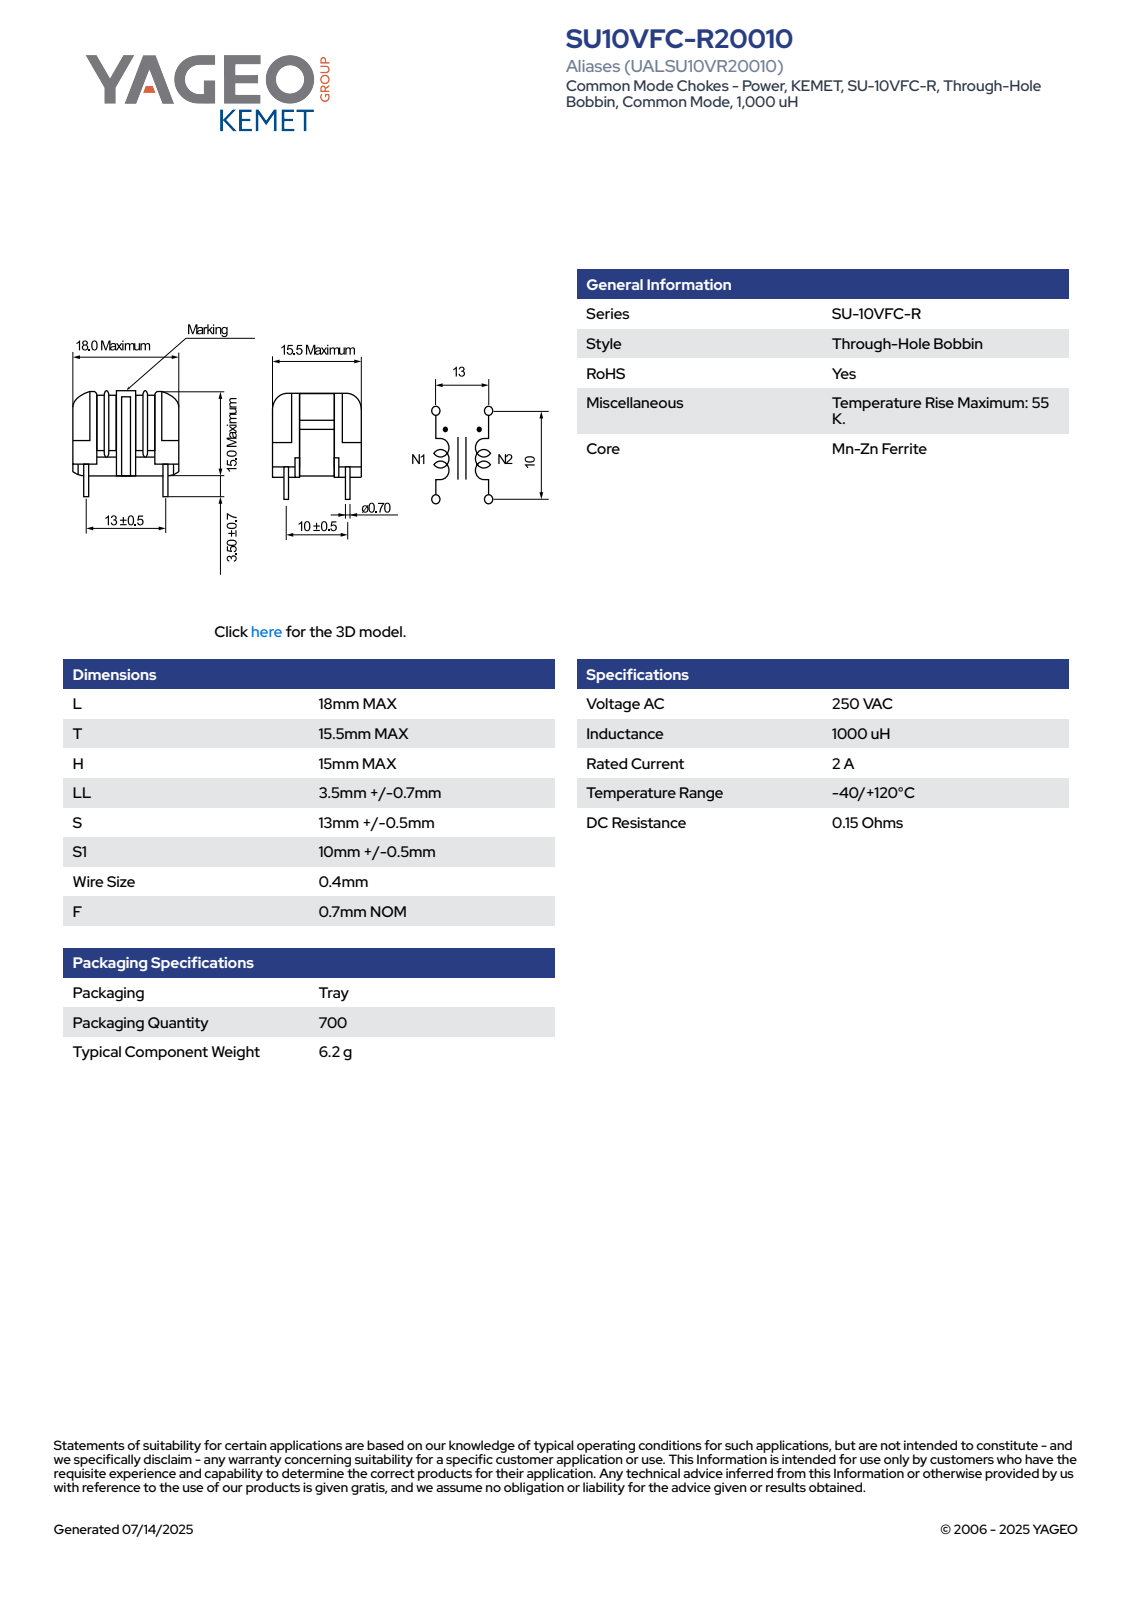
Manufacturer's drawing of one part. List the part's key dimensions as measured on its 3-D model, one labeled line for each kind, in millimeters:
Part name (STEP PRODUCT): SU10VFC(MAX-LOGO)
STEP written by: SolidWorks 2018 (AUTOMOTIVE_DESIGN)
Units: millimetres
Bodies: 2 solids, 912 faces (302 planar, 394 cylindrical, 216 other)
Overall size (bounding box): 18.5 × 18 × 15.5
Volume: 2 381 mm³ · Surface area: 3 995 mm²
Round bosses / shafts (diameter × count): ⌀0.7 ×4
Partial cylindrical surfaces — rounded edges, fillets, slot ends (radius × count): R0.5 ×60, R0.2 ×48, R0.23 ×48, R0.3 ×38, R0.8 ×10, R0.55 ×4, R2 ×4, R2.5 ×4
Main face-to-face distances: 6.5, 1.7, 7.1, 5.35, 7.2, 4.55, 1.5, 0.9, 0.6, 2.6
